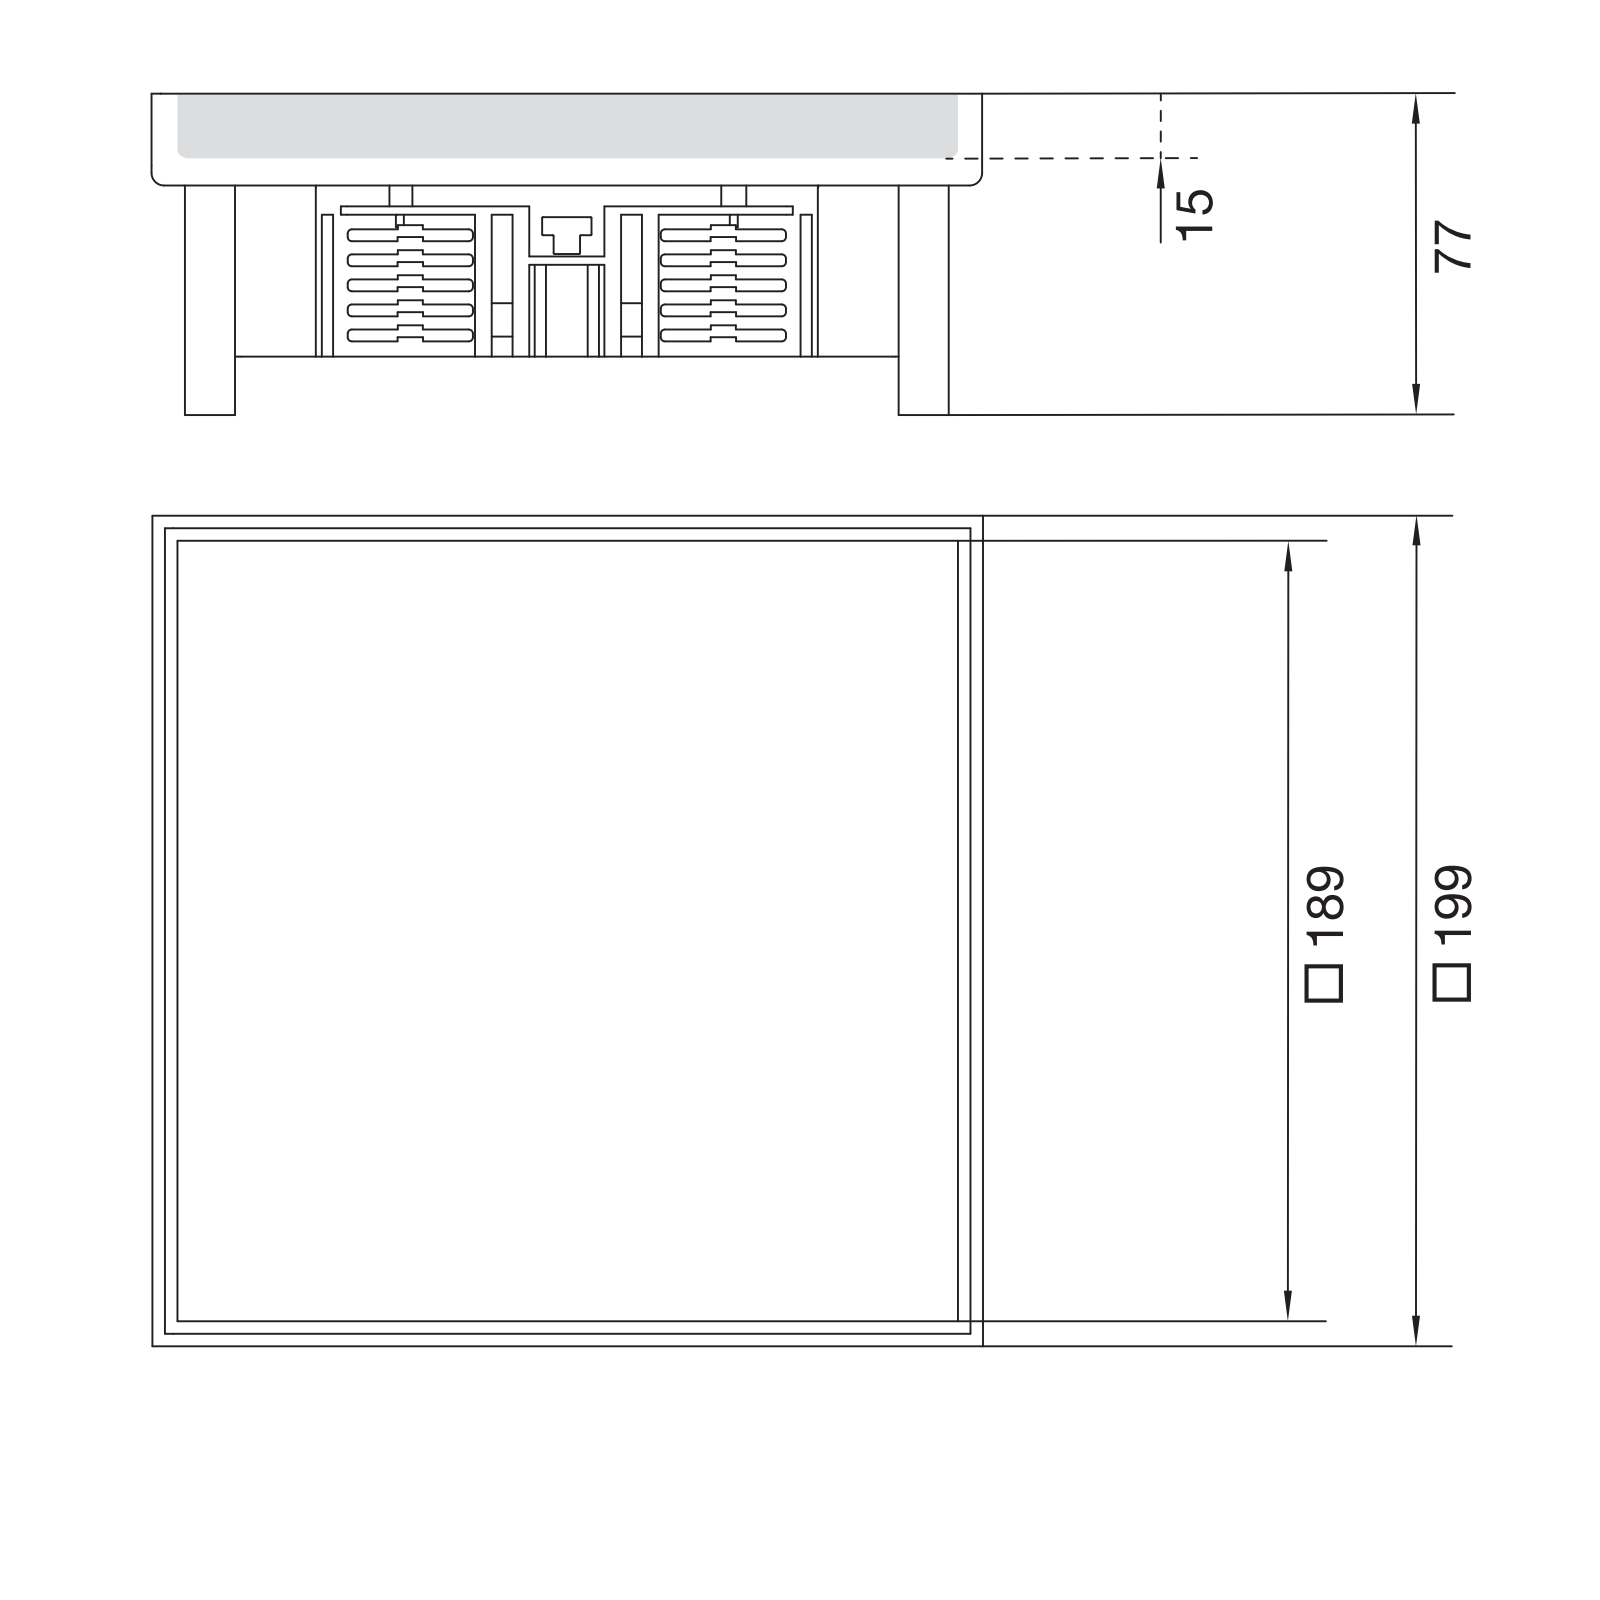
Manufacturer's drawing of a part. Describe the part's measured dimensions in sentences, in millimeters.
The part is named "T-00596_1; T-00595_1; T-00805_ASM_1_ASM; U09001_1 (+4 more)". Its 3-D file was written by "CREO PARAMETRIC BY PTC INC, 2022281 (AUTOMOTIVE_DESIGN)". It is 7 solids with 181 faces: 121 planar, 60 cylindrical and 0 other. Overall it measures 199 by 199 by 77 millimeters. Its volume is 229 156 cubic millimeters and its surface area 228 190 square millimeters. Round holes: 4 of diameter 6.8, 4 of diameter 8.5. Round bosses or shafts: 4 of diameter 12, 4 of diameter 9.85. Partial cylindrical surfaces (rounded edges, fillets, slot ends): 8 of radius 1, 8 of radius 3, 5 of radius 105, 1 of radius 107. The main face-to-face distances are 2, 5, 3, 2.5, 194, 174.5, 197, 7, 153.5, 1. The hole center spacings are 171, 241.83.
